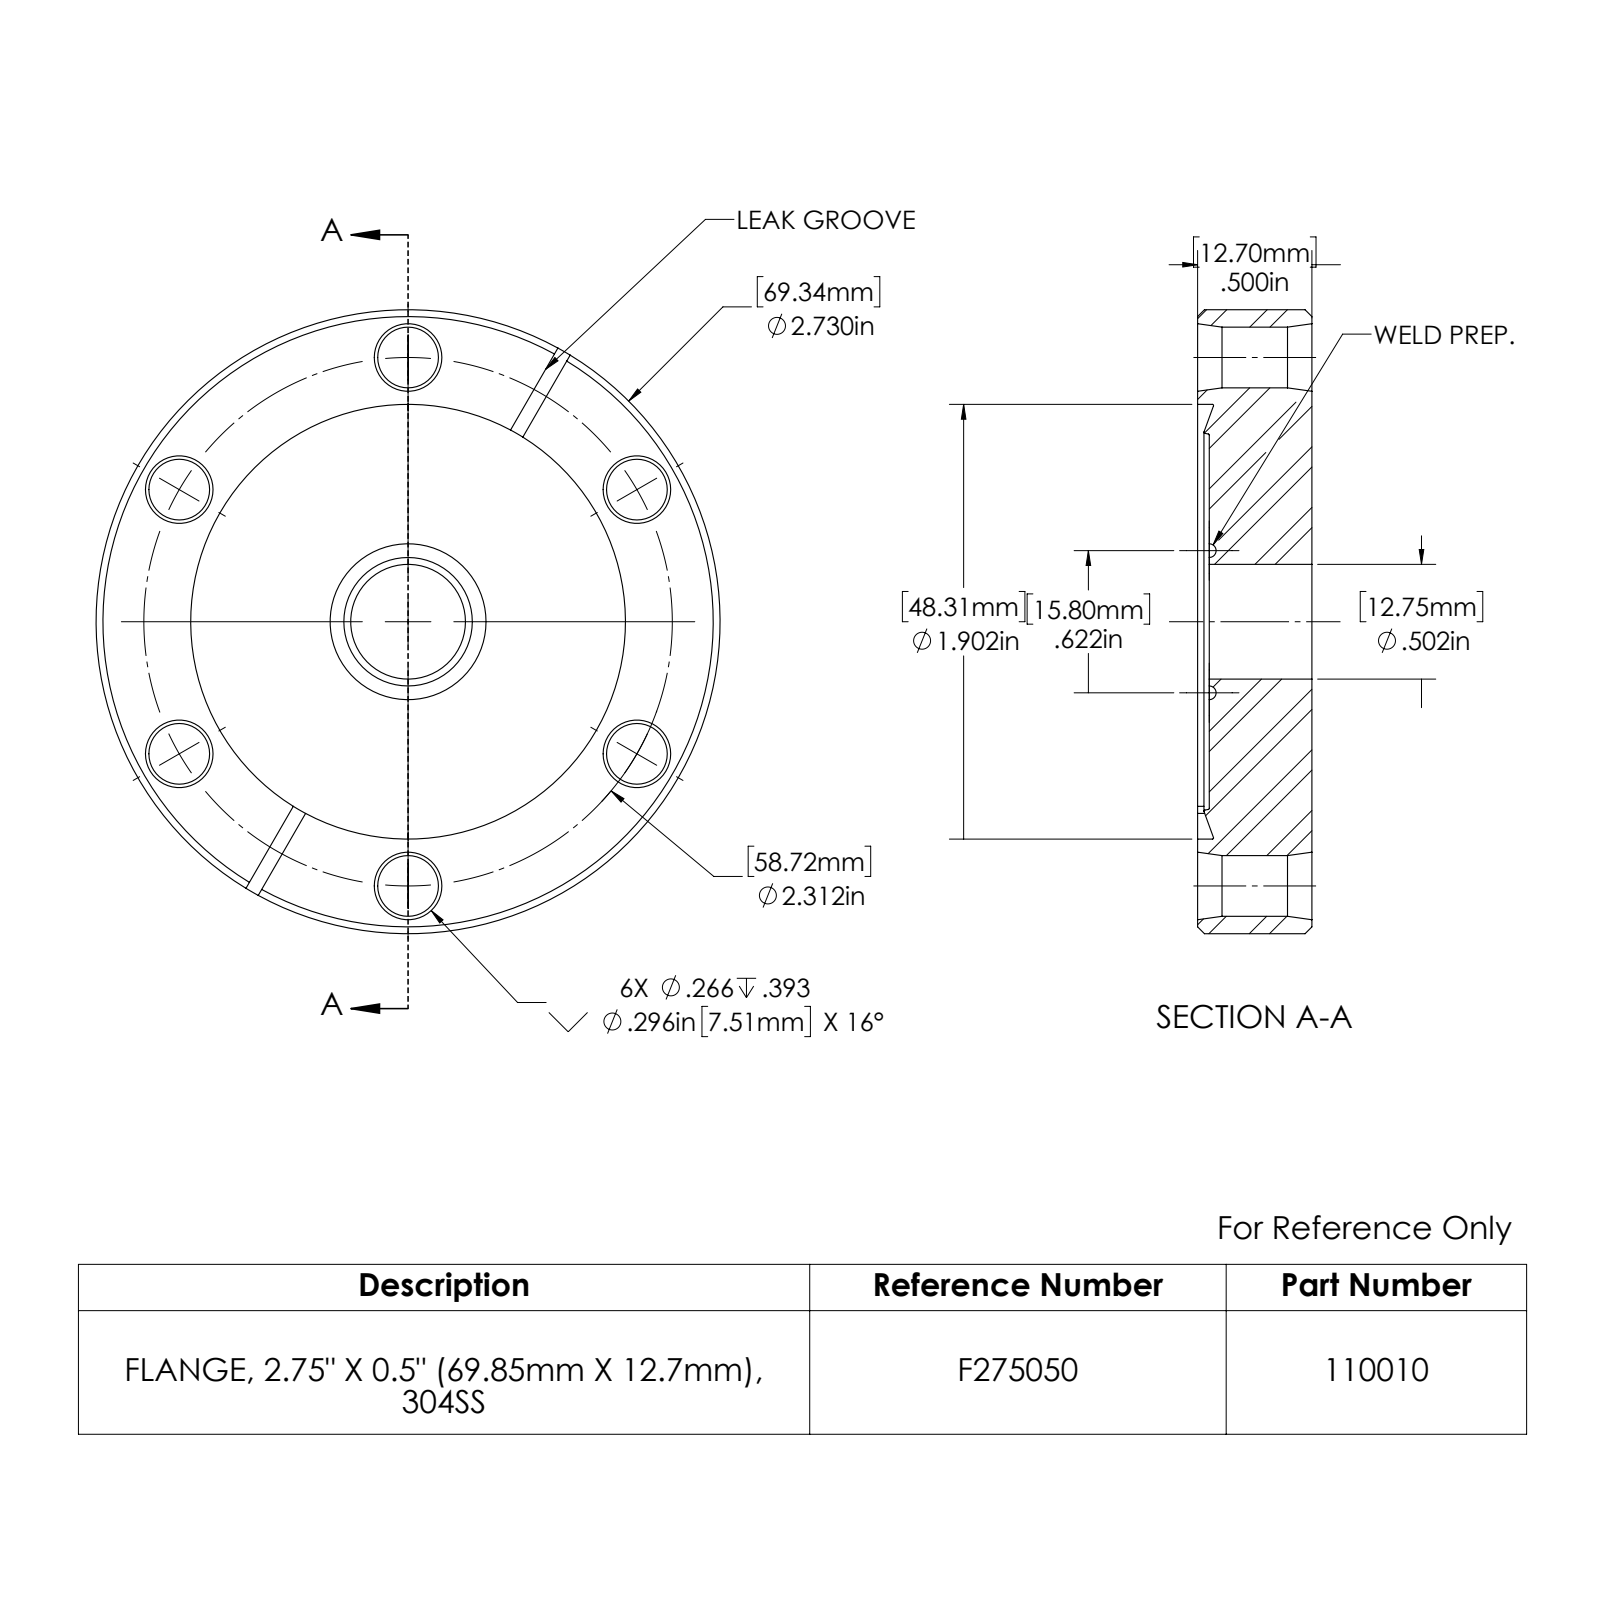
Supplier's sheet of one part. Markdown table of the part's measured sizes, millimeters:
| quantity | value |
| --- | --- |
| part name | 110010 |
| STEP written by | SolidWorks 2022 (AUTOMOTIVE_DESIGN) |
| units | millimeters |
| bodies | 1 solid, 70 faces (11 planar, 18 cylindrical, 41 other) |
| overall size | 69.3 × 69.3 × 12.7 |
| volume | 41 080 mm³ |
| surface area | 11 890 mm² |
| round holes (diameter × count) | 6.8 × 6, 12.8 × 1, 48.3 × 1 |
| round bosses / shafts (diameter × count) | 69.3 × 1 |
| main face-to-face distances | 12.7, 1.3, 11.4, 1.3, 11.4, 1.6 |
| hole center spacings | 29.4, 50.9, 50.9, 58.7, 58.7 |
